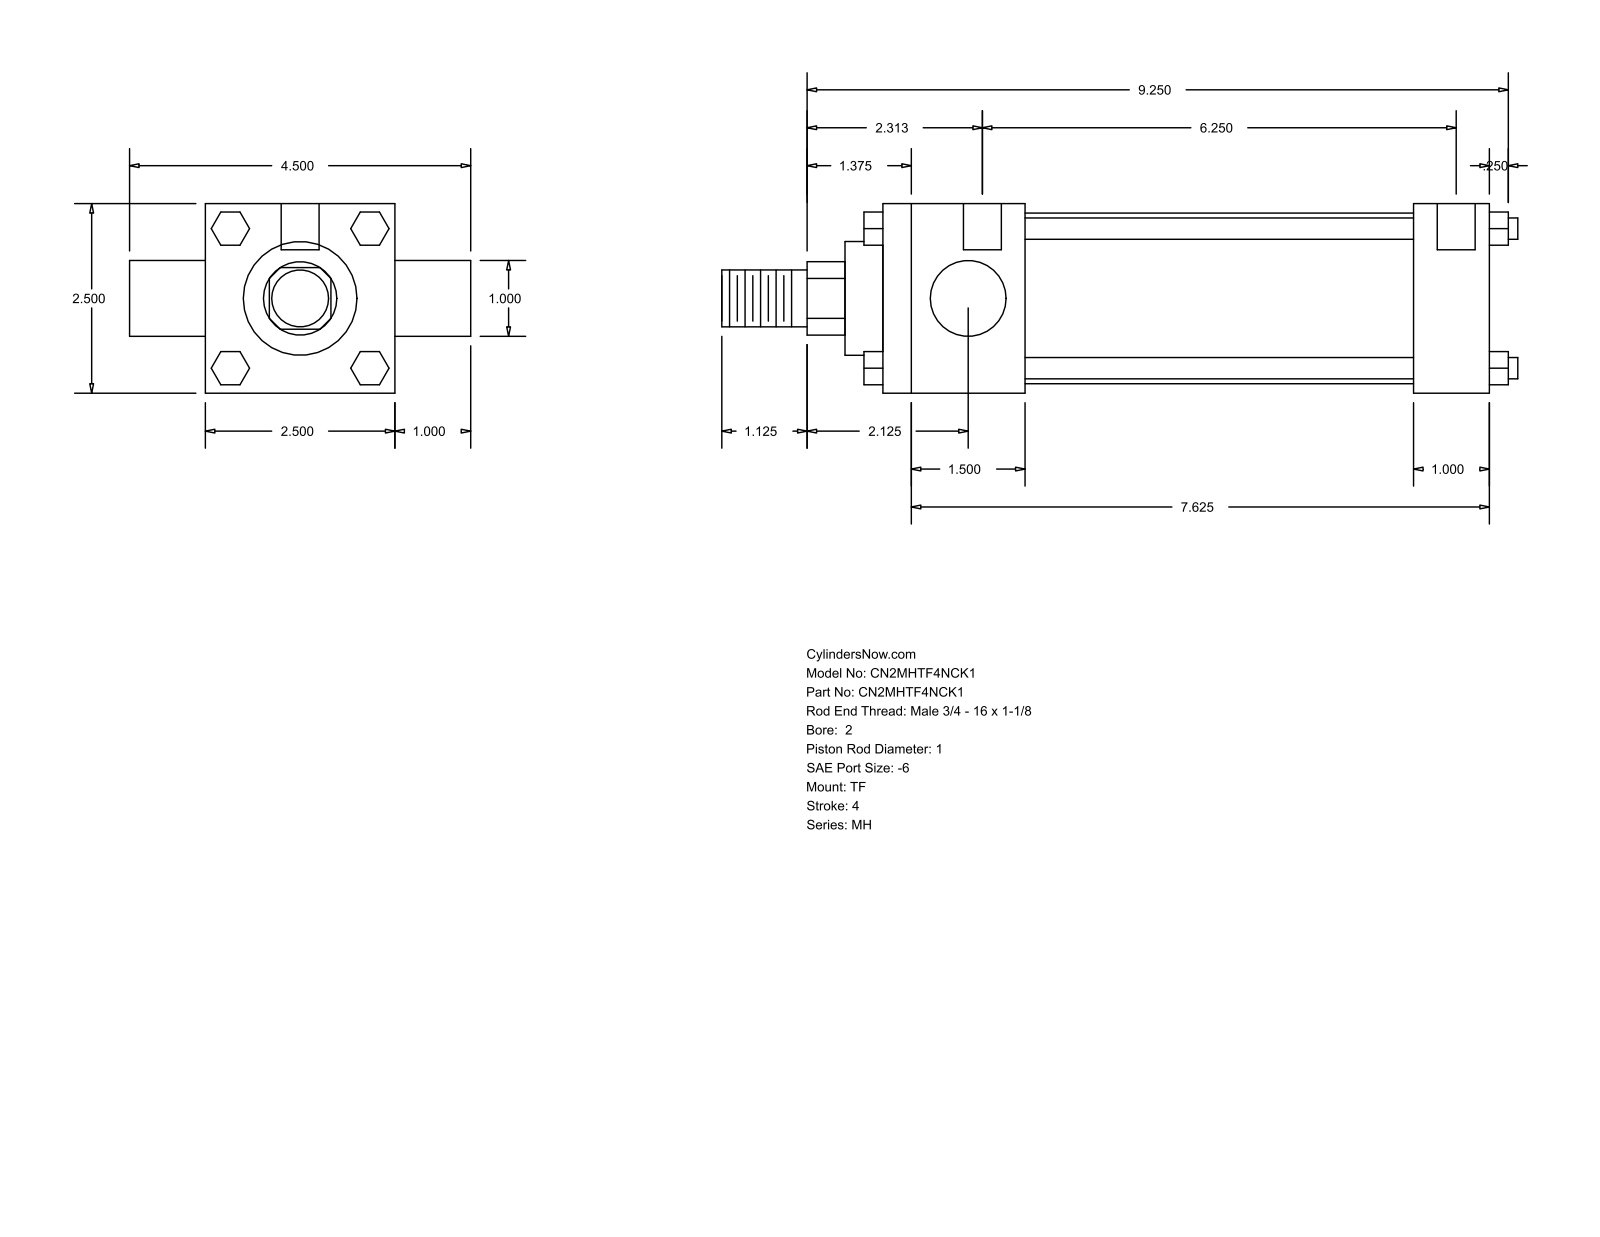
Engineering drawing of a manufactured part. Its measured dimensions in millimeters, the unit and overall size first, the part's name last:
Units: millimetres
Overall size (bounding box): 266.7 × 114.3 × 63.5
Round holes (diameter × count): ⌀5.56 ×3, ⌀12.7 ×2
Round bosses / shafts (diameter × count): ⌀7.14 ×4, ⌀25.4 ×2, ⌀57.15 ×1, ⌀38.1 ×1, ⌀19.05 ×1
Partial cylindrical surfaces — rounded edges, fillets, slot ends (radius × count): R12.29 ×1
Main face-to-face distances: 63.5, 203.2, 25.4, 47.63, 177.8, 130.17, 155.57, 88.9, 215.9, 6.35
Hole centre spacings: 3.17, 4.76, 158.75, 161.92, 163.51, 166.68
Bodies: 0 solids, 120 faces (92 planar, 28 cylindrical, 0 other)
Part name (STEP PRODUCT): MH_TF__0200_1
STEP written by: GSSL Pune (CONFIG_CONTROL_DESIGN)
